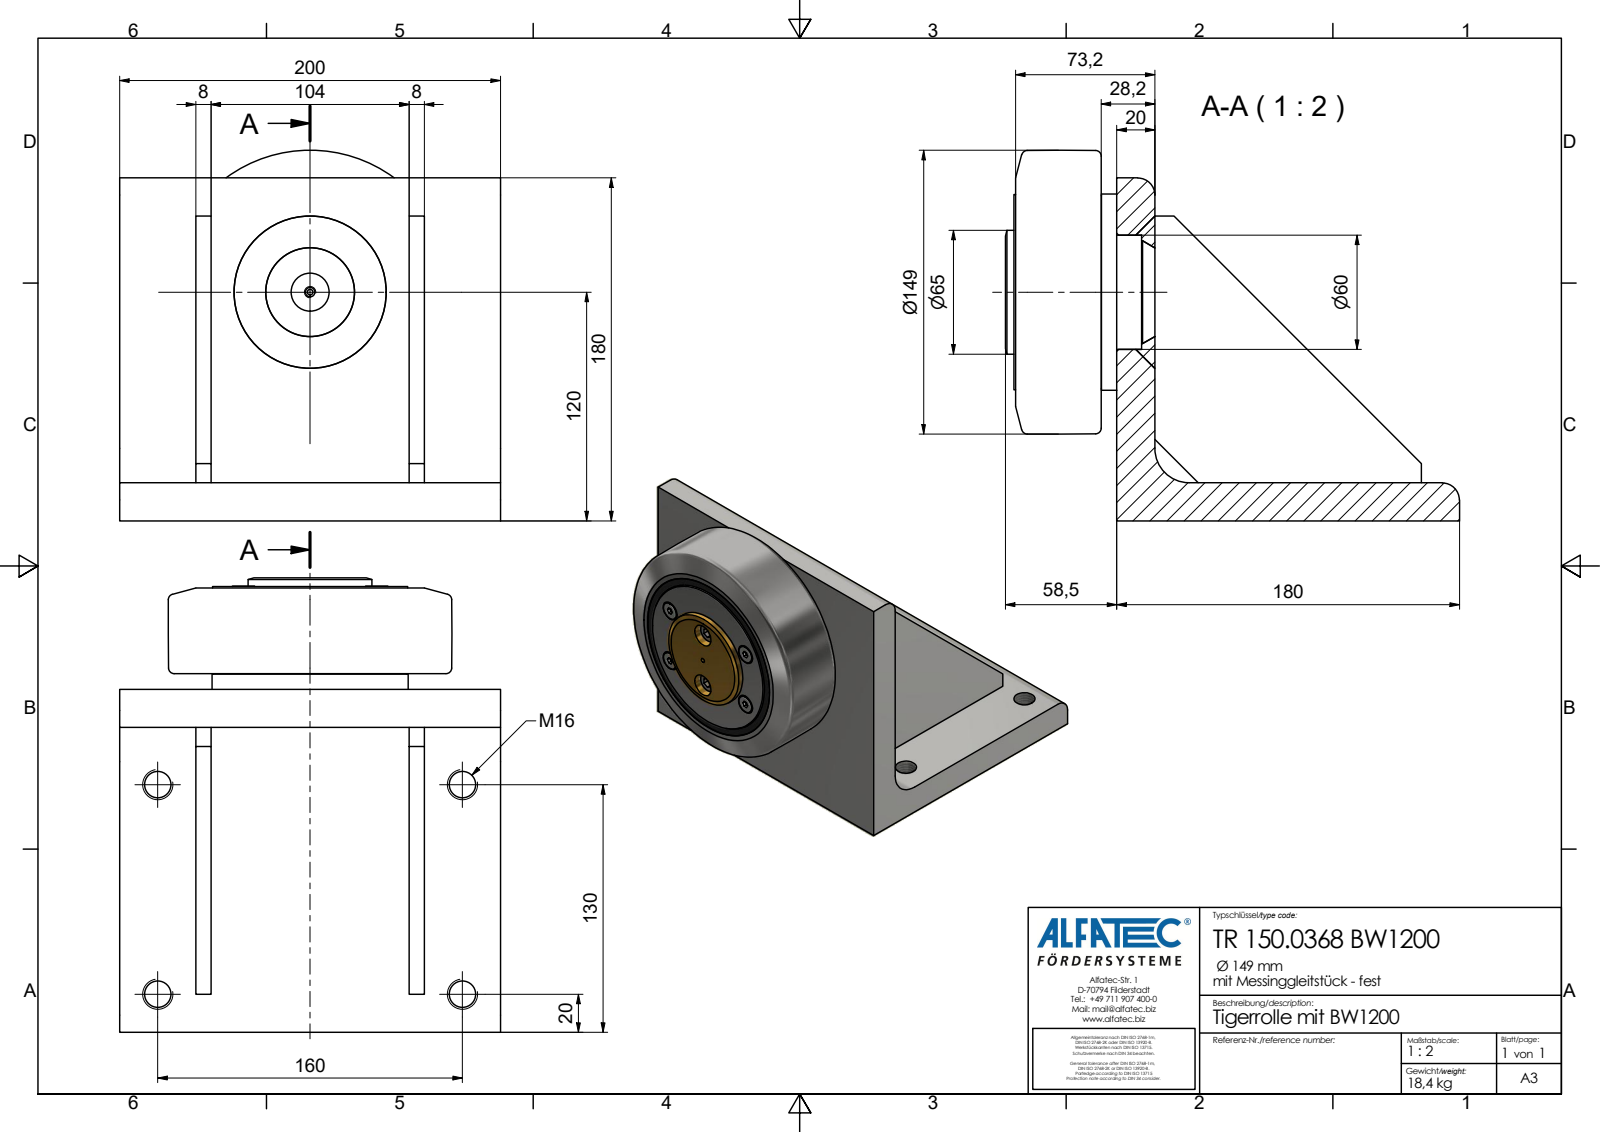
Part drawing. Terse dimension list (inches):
name: TR 150.0368 BW1200_Kontur
written by: Autodesk Inventor 2020 (AP242_MANAGED_MODEL_BASED_3D_ENGINEERING_MIM_LF)
unit: in
bodies: 1 solid, 105 faces (76 planar, 18 cylindrical, 11 other)
size: 9.39 × 7.874 × 7.657
volume: 145.7 in³; area: 375.1 in²
holes: 4× ⌀0.545, 2× ⌀0.591, 1× ⌀0.118
bosses: 4× ⌀0.461, 1× ⌀4.055, 1× ⌀4.035, 1× ⌀3.992, 1× ⌀2.559
rounds: 2× R0.354, 1× R0.709
face distances: 0.787, 0.315, 4.409, 6.299, 1.575, 1.89, 5.984, 4.094, 4.724, 0.323
hole spacings: 0.787, 4.331, 6.299, 7.644, 1.575
